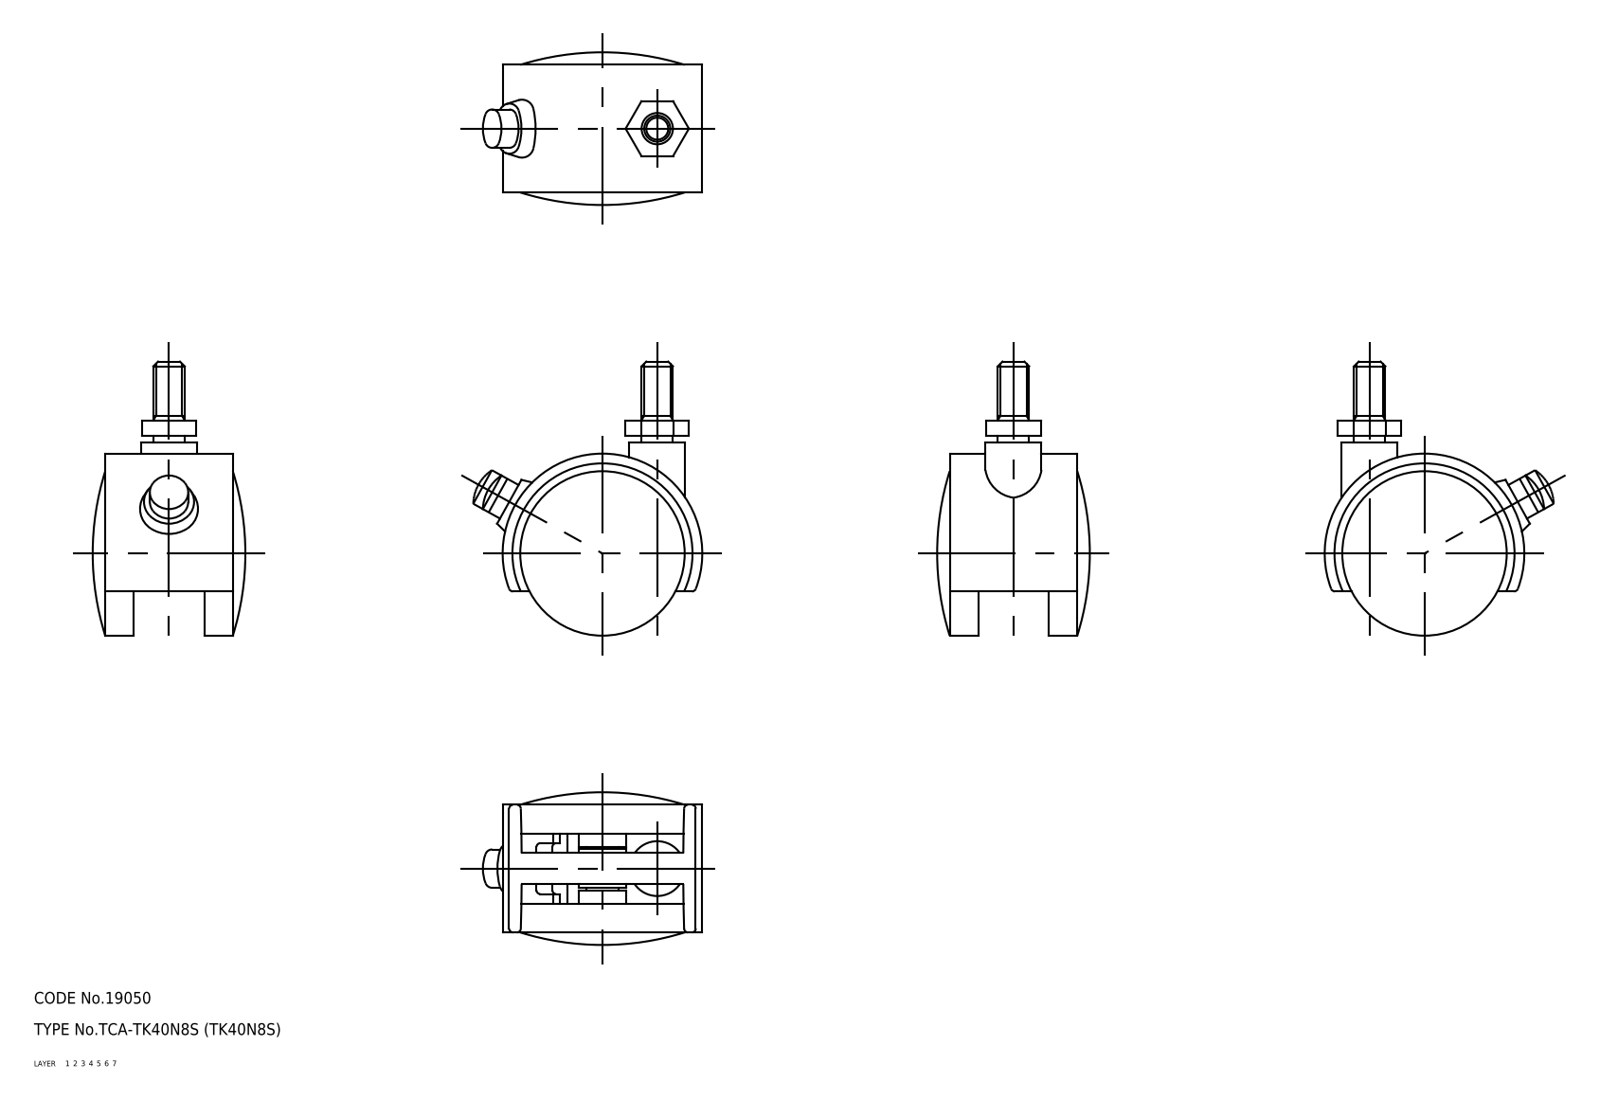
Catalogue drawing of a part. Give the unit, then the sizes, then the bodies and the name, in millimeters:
Units: millimetres
Overall size (bounding box): 70 × 56.05 × 39
Volume: 40 780 mm³ · Surface area: 22 102 mm²
Bodies: 4 solids, 124 faces (0 planar, 0 cylindrical, 124 other)
Part name (STEP PRODUCT): wheel; main shaft; TK40N8S_4284_36
STEP written by: CADfix (AUTOMOTIVE_DESIGN)
